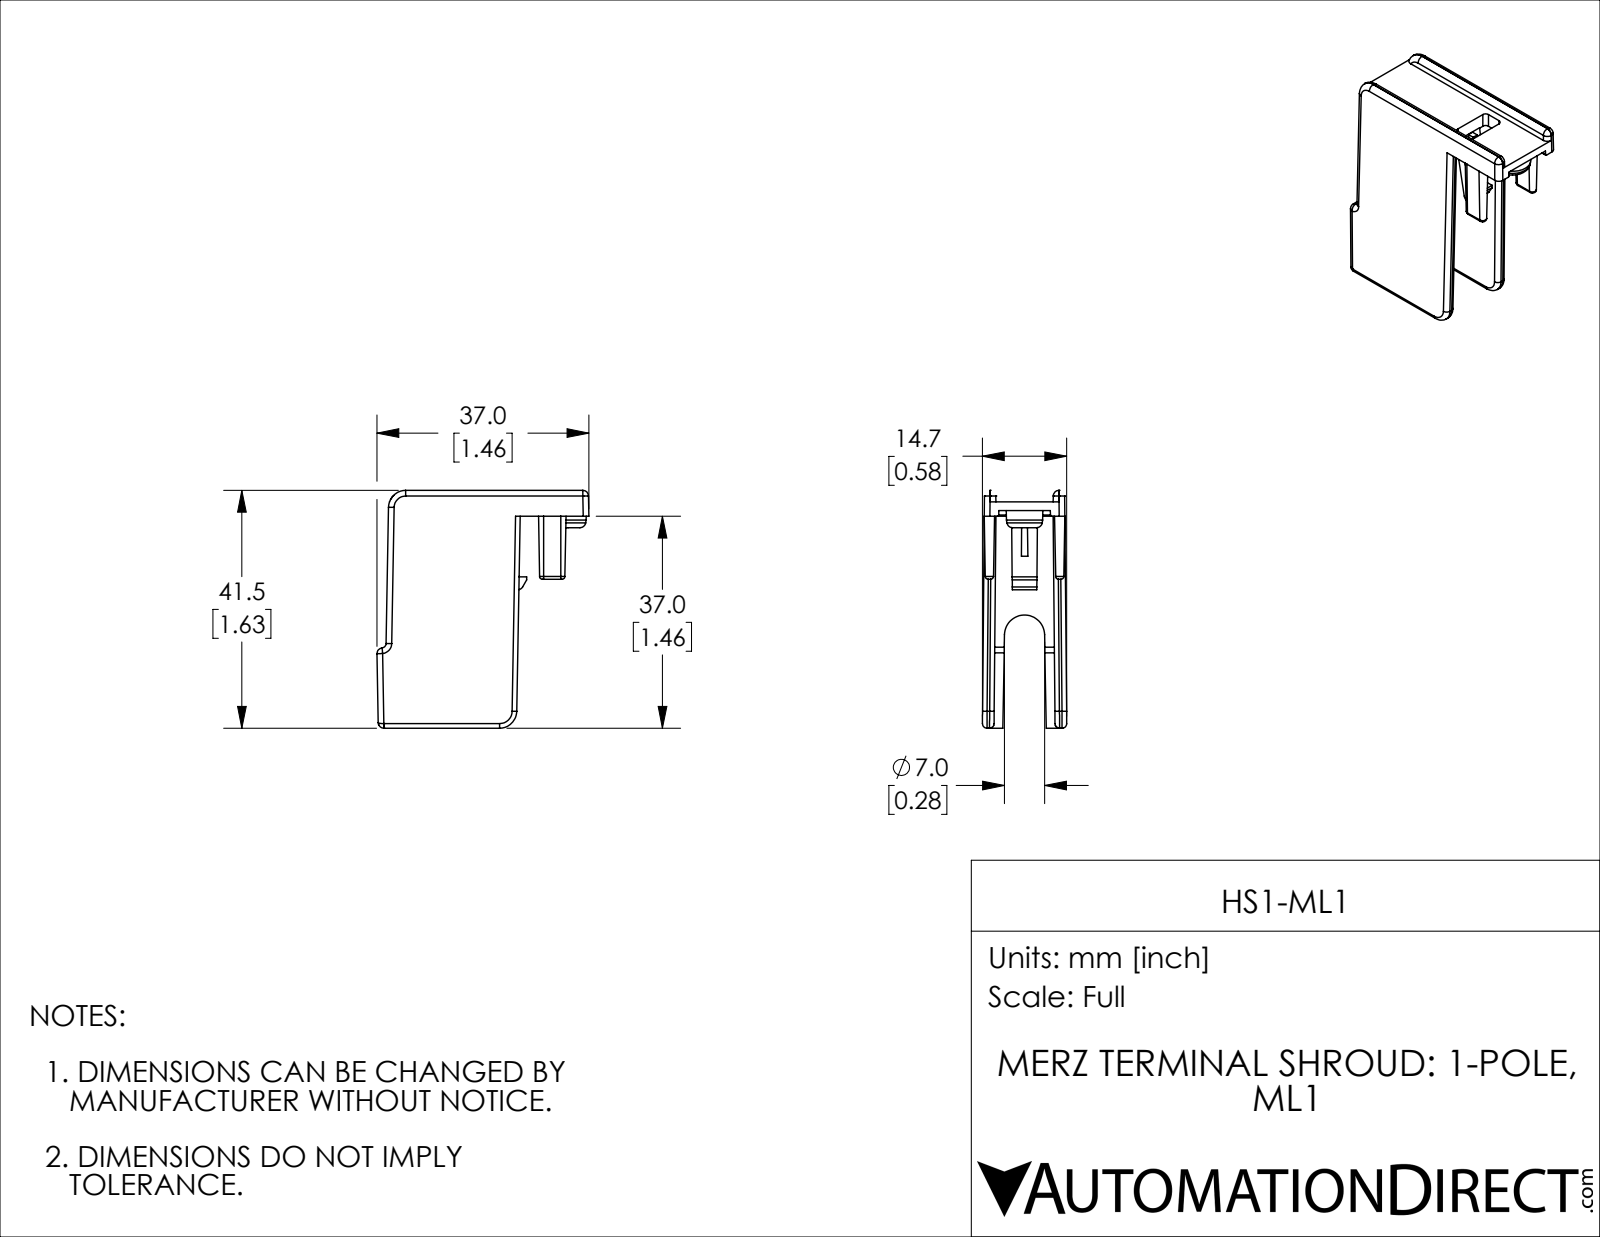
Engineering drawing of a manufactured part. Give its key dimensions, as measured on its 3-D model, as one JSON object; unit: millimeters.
{"part_name": "HS1-ML1", "step_written_by": "SolidWorks 2019 (AUTOMOTIVE_DESIGN)", "units": "millimeters", "bodies": {"solids": 1, "faces": 138, "planar": 53, "cylindrical": 47, "other": 38}, "overall_size": [41.5, 37, 14.7], "volume_mm3": 5770, "surface_area_mm2": 5981, "partial_cylinders_radius": [[1, 14], [0.8, 9], [0.5, 4], [0.7, 4], [1, 3], [0.2, 2], [3, 2], [3.5, 1]], "face_to_face_distances": [2, 2.5, 1.5, 10.2, 12.3, 2.1, 2, 7.2, 9.3, 1]}
